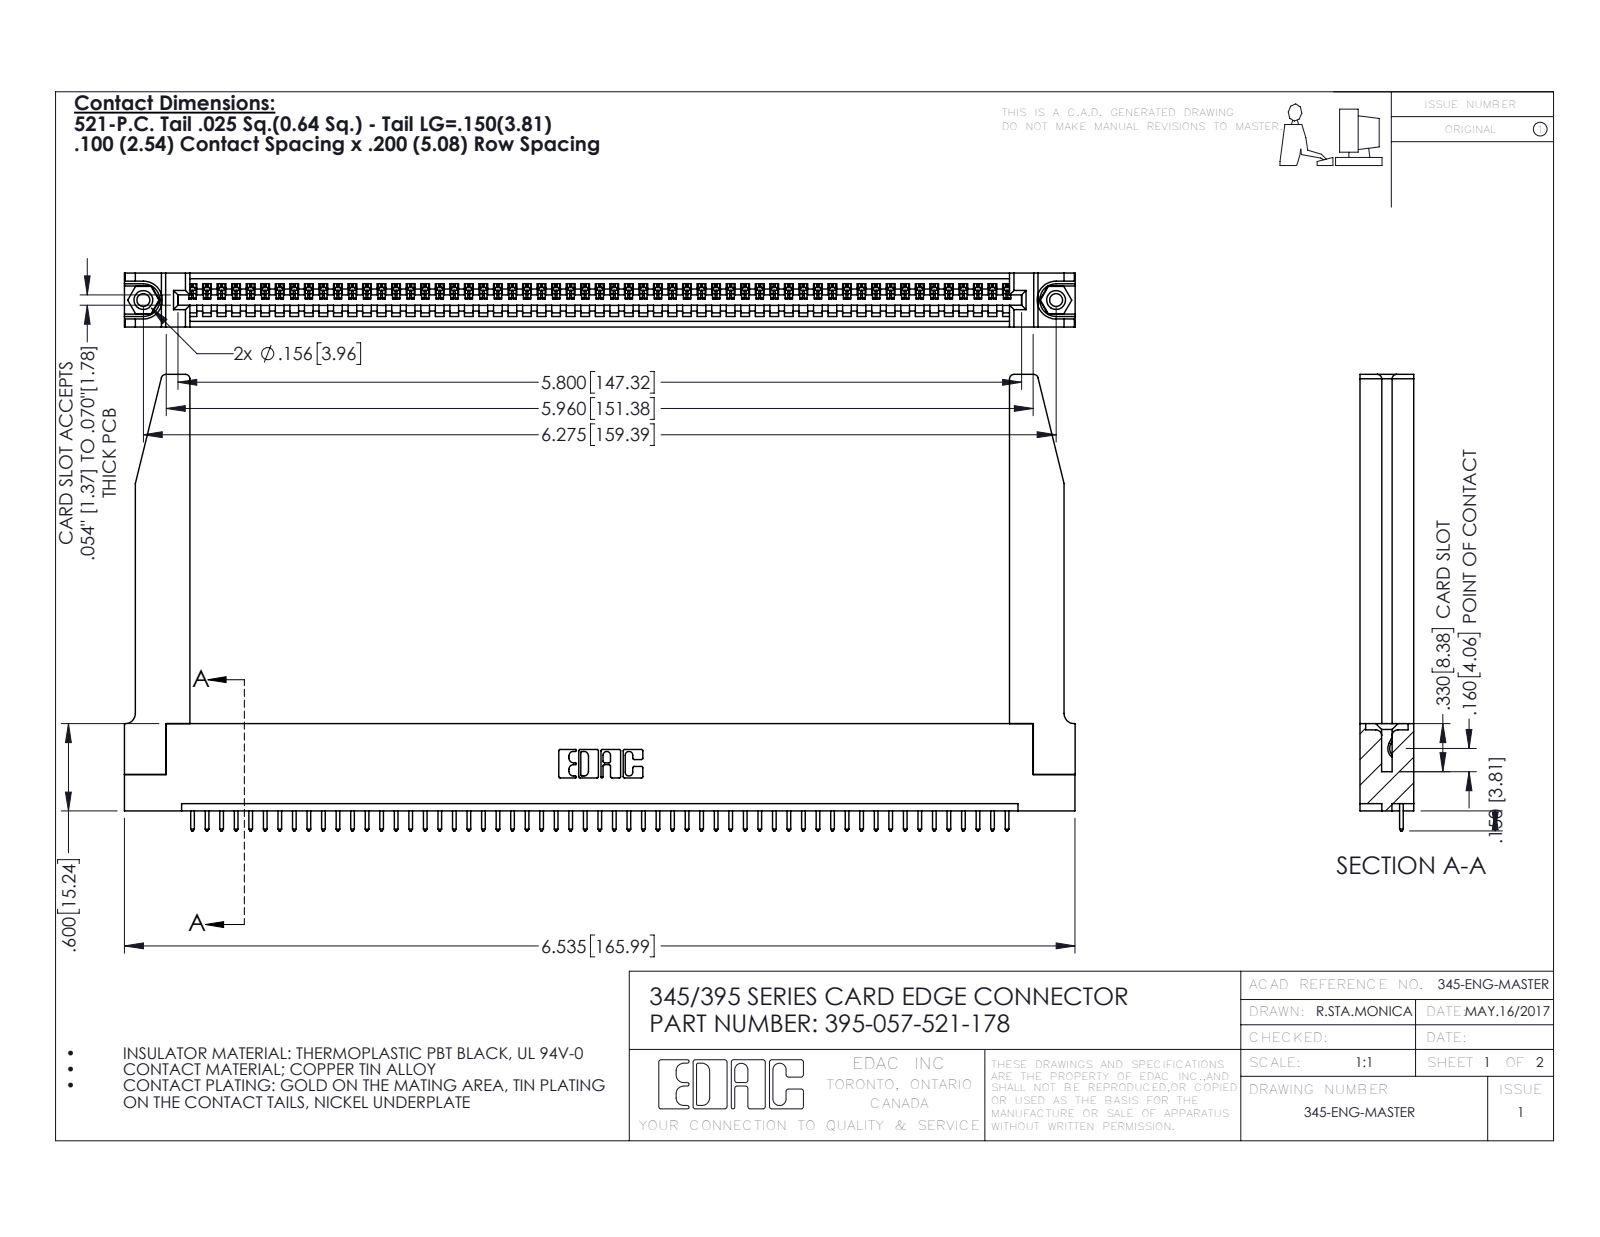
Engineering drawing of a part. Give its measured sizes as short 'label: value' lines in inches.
name: 395-057-521-178; 345 Part_Flush Mounting Lugs - 0.156 Dia-TH; 345-250-001_345-250-001-102; 345-220-078_345-220-078 (+1 more)
written by: SolidWorks 2016 (CONFIG_CONTROL_DESIGN)
unit: in
bodies: 62 solids, 3666 faces (2502 planar, 1112 cylindrical, 52 other)
size: 6.536 × 3.137 × 0.37
volume: 1.434 in³; area: 42.34 in²
holes: 2× ⌀0.089, 2× ⌀0.125, 2× ⌀0.156, 1× ⌀0.064
bosses: 2× ⌀0.155
rounds: 114× R0.006, 114× R0.01, 22× R0.01, 8× R0.03, 6× R0.007, 6× R0.031, 3× R0.026, 2× R0.031
face distances: 0.37, 0.072, 0.298, 0.2, 0.098, 0.272, 0.025, 0.225, 0.148, 0.15
hole spacings: 0.27, 6.039, 6.275
